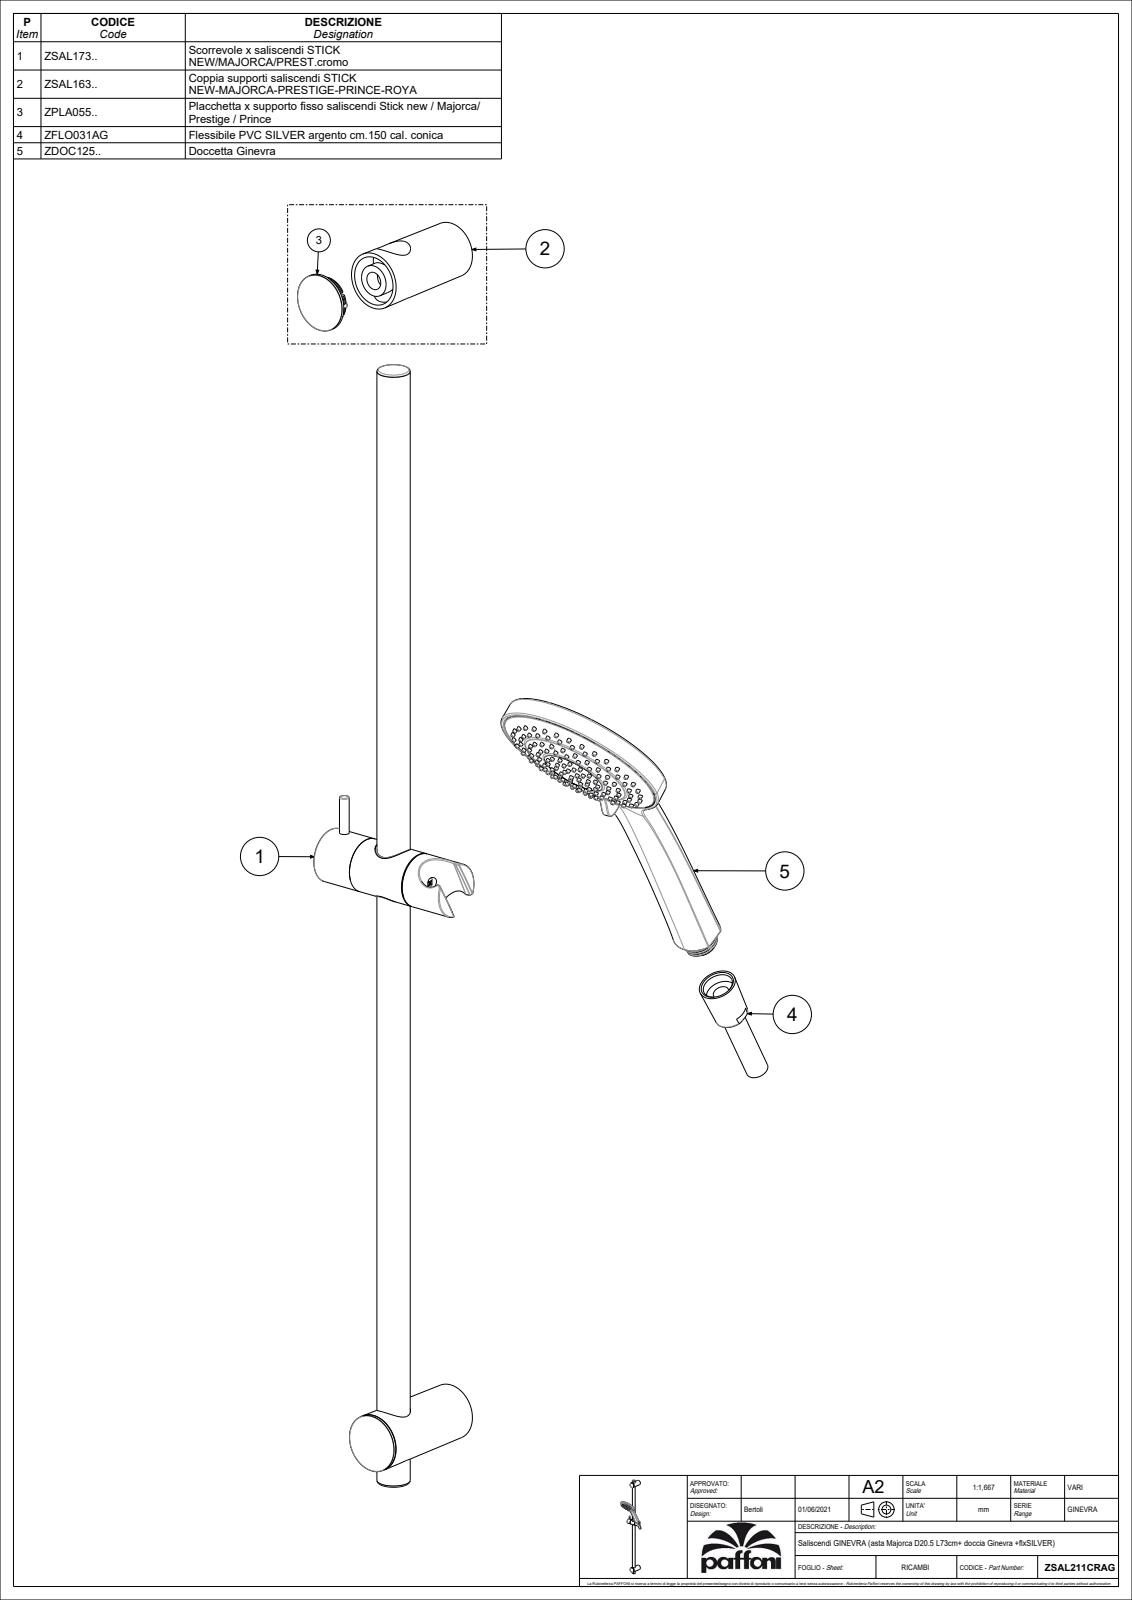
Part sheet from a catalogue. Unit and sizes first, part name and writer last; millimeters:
Units: millimetres
Overall size (bounding box): 734 × 218.68 × 147.08
Round holes (diameter × count): ⌀2.3 ×3, ⌀31 ×3, ⌀5.4 ×2, ⌀8 ×2, ⌀11.2 ×2, ⌀22.5 ×2, ⌀3.8 ×1, ⌀10 ×1, ⌀11 ×1, ⌀14 ×1, ⌀18 ×1, ⌀20 ×1
Round bosses / shafts (diameter × count): ⌀4.67 ×71, ⌀4.4 ×30, ⌀4.66 ×25, ⌀5.6 ×3, ⌀36.5 ×2, ⌀35 ×2, ⌀22.4 ×2, ⌀12 ×2
Partial cylindrical surfaces — rounded edges, fillets, slot ends (radius × count): R0.5 ×94, R1 ×64, R0.3 ×50, R0.8 ×37, R1.5 ×9, R0.6 ×8, R2 ×6, R3 ×4
Main face-to-face distances: 1.1, 366.51, 367.61, 365.41, 1.5, 2, 68.2, 1, 70.2, 3.1
Hole centre spacings: 22.77, 28.5, 14, 45, 570
Volume: 460 243 mm³ · Surface area: 237 602 mm²
Bodies: 5 solids, 3802 faces (806 planar, 747 cylindrical, 2249 other)
Part name (STEP PRODUCT): ZSAL211CRAG
STEP written by: CREO PARAMETRIC BY PTC INC, 2020044 (CONFIG_CONTROL_DESIGN)
